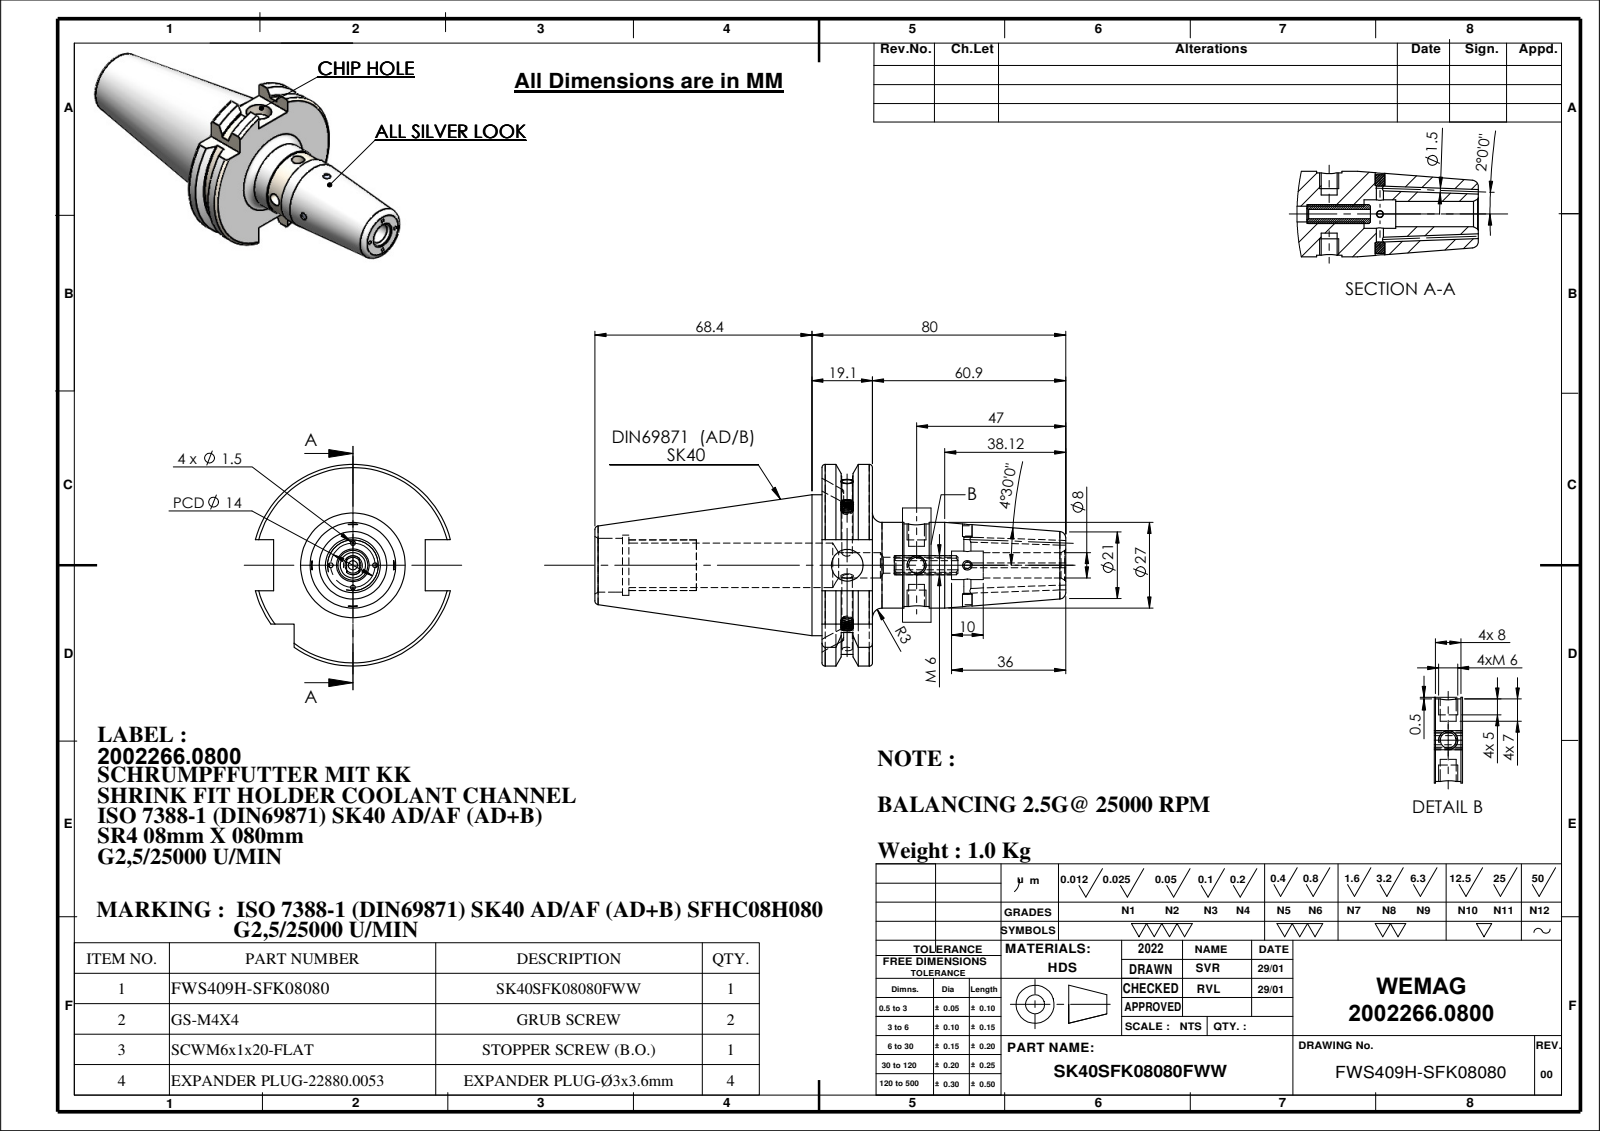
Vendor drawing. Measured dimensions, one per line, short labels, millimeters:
name: GS-M4X4_DIN 913 - M4 x 4-N; SK40SFK08080FWW; EXPANDER PLUG Ø3x3.6; 91406-SR408080 (+1 more)
written by: SolidWorks 2018 (CONFIG_CONTROL_DESIGN)
unit: mm
bodies: 8 solids, 291 faces (66 planar, 105 cylindrical, 120 other)
size: 148.4 × 63.55 × 61.48
volume: 126 638 mm³; area: 29 333 mm²
holes: 4× ⌀1.5, 3× ⌀5, 2× ⌀2.2, 2× ⌀3, 1× ⌀2.9, 1× ⌀3.3, 1× ⌀7.99, 1× ⌀8, 1× ⌀8.99, 1× ⌀10, 1× ⌀14, 1× ⌀17
bosses: 2× ⌀4, 1× ⌀44.45, 1× ⌀27, 1× ⌀26
rounds: 1× R3, 1× R28.12, 1× R31.77
face distances: 15.9, 60.9, 76.8, 16.1, 47.8, 4, 71.6, 87.5, 148.4, 10.7
hole spacings: 16, 21.85, 37.85
